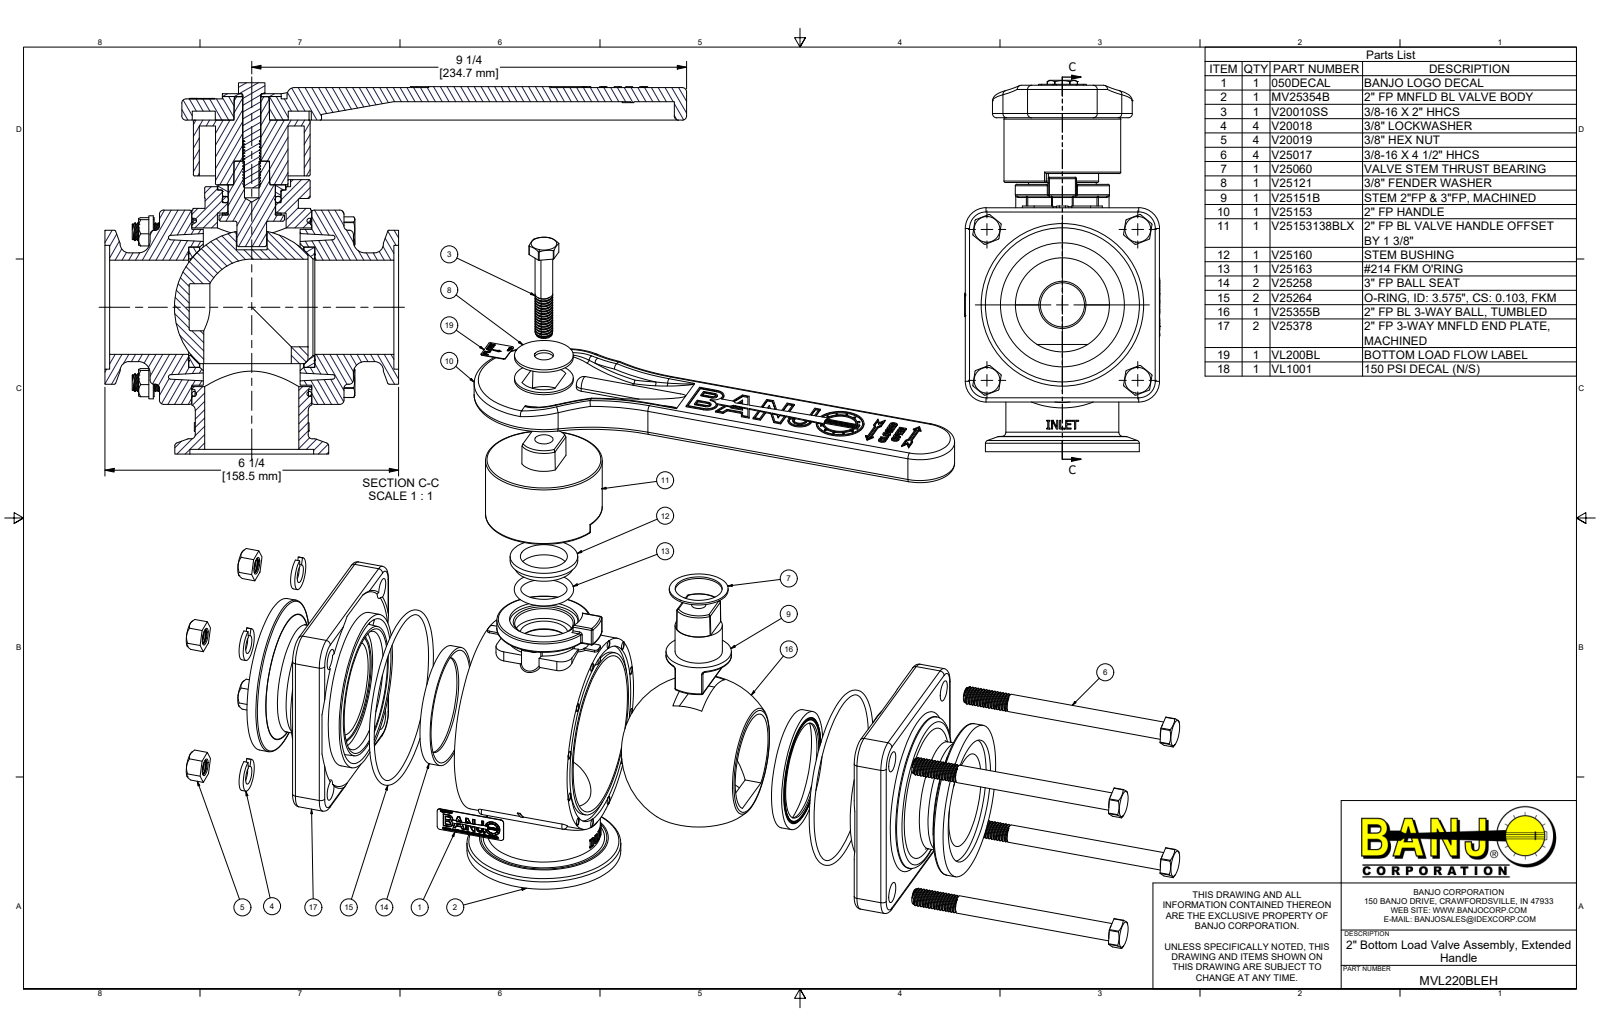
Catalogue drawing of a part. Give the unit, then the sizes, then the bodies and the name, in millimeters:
Units: millimetres
Overall size (bounding box): 313.9 × 200.3 × 105.2
Round holes (diameter × count): ⌀4.3 ×12, ⌀7.8 ×4, ⌀9.8 ×4, ⌀11.1 ×4, ⌀25.4 ×2, ⌀50.8 ×2, ⌀51.8 ×2, ⌀66.8 ×2, ⌀5.8 ×1, ⌀7.8 ×1, ⌀8.2 ×1, ⌀9.9 ×1
Round bosses / shafts (diameter × count): ⌀8.2 ×75, ⌀9.5 ×5, ⌀17.4 ×4, ⌀83.1 ×2, ⌀104.8 ×1, ⌀88.9 ×1, ⌀84.1 ×1, ⌀75.4 ×1
Partial cylindrical surfaces — rounded edges, fillets, slot ends (radius × count): R2.3 ×26, R0.8 ×23, R1.5 ×12, R1.6 ×12, R0.8 ×10, R4.1 ×10, R6.4 ×5, R8.1 ×5
Main face-to-face distances: 17.4, 82.2, 2.5, 45.2, 104.8, 64.8, 110.7, 17.5, 15.7, 83.8
Hole centre spacings: 50.2, 71, 97, 26, 28.8, 54.3, 76.4, 87
Volume: 1 030 000 mm³ · Surface area: 320 200 mm²
Bodies: 31 solids, 4754 faces (2520 planar, 621 cylindrical, 1613 other)
Part name (STEP PRODUCT): MVL220BLEH; MV25354B; VL1000; V25355B (+8 more)
STEP written by: Autodesk Inventor 2019 (AUTOMOTIVE_DESIGN)
